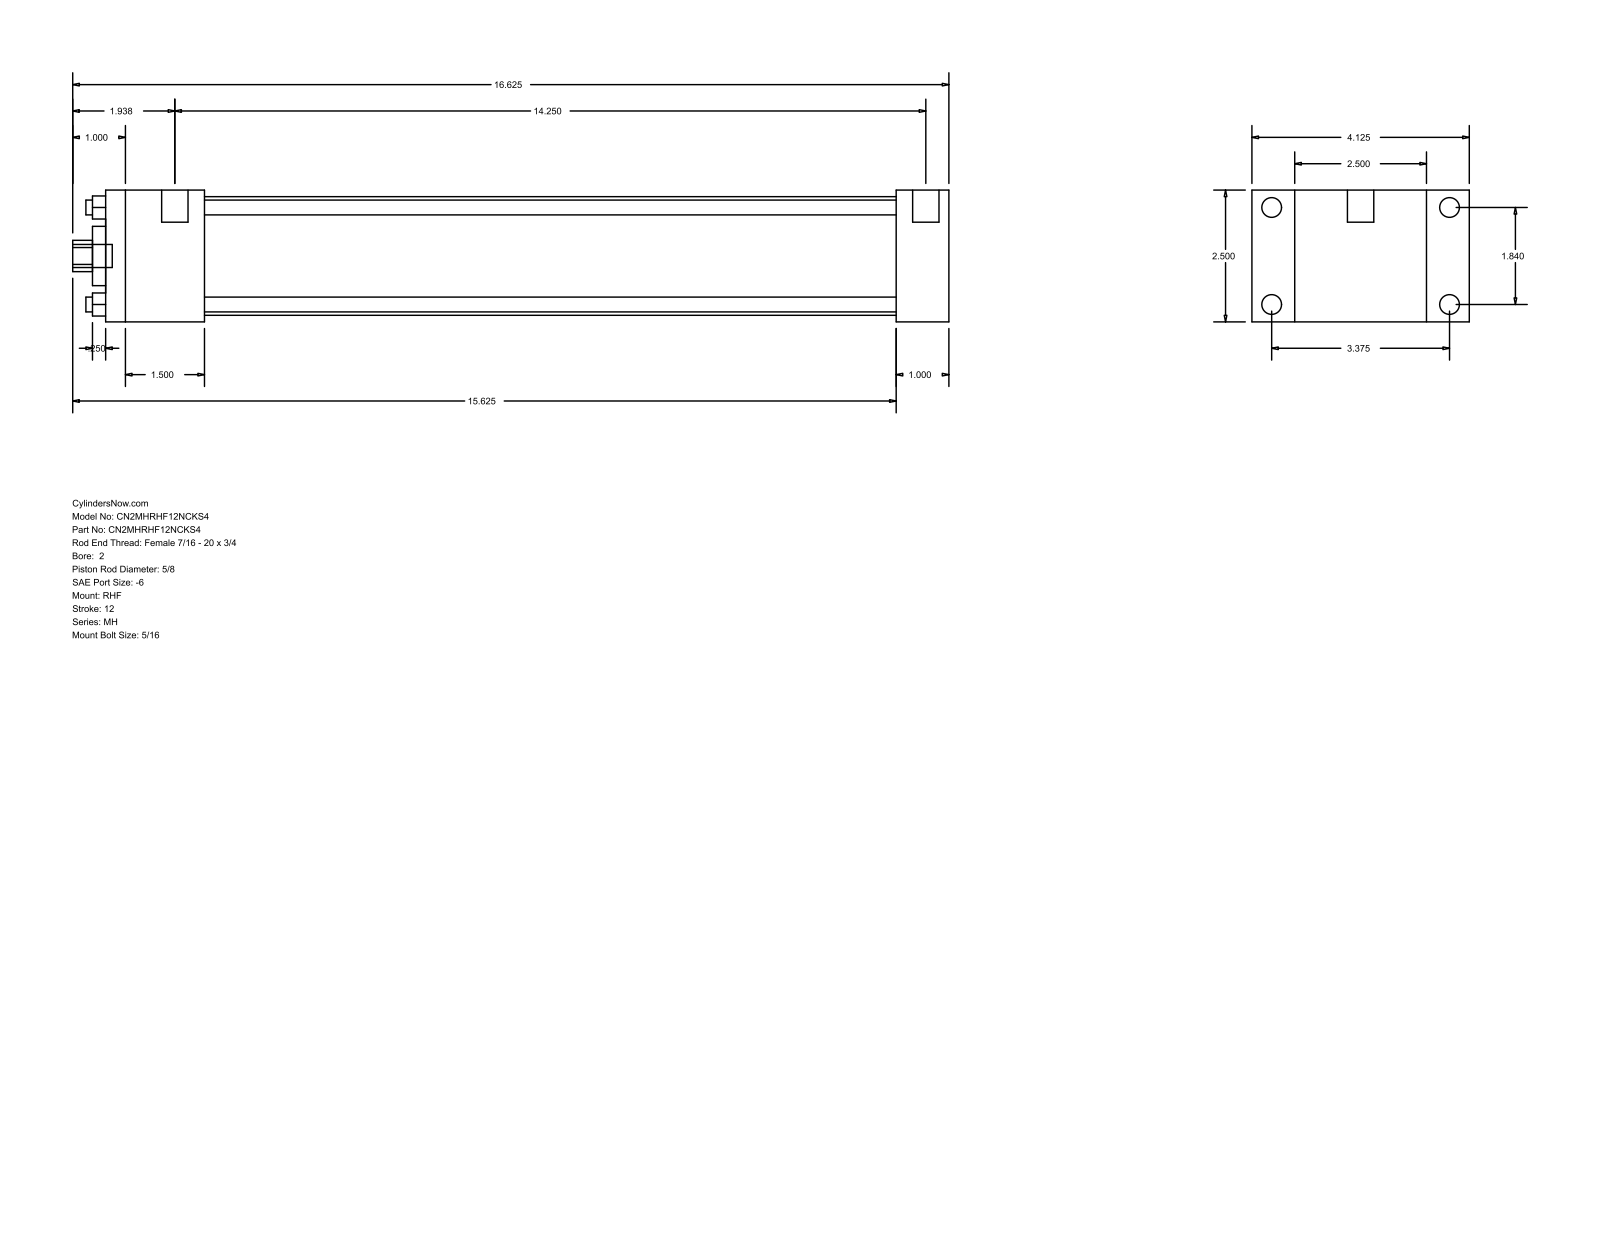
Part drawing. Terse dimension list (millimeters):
name: MH_RHF__0200_0.625
written by: GSSL Pune (CONFIG_CONTROL_DESIGN)
unit: mm
bodies: 0 solids, 88 faces (60 planar, 28 cylindrical, 0 other)
size: 422.27 × 104.78 × 63.5
holes: 4× ⌀7.14, 1× ⌀15.88, 1× ⌀28.57, 1× ⌀57.15
bosses: 4× ⌀9.53, 4× ⌀5.56, 2× ⌀12.7, 1× ⌀11.11
rounds: 1× R7.54
face distances: 63.5, 25.39, 20.64, 84.14, 381, 406.39, 104.78, 47.62, 333.38, 358.77
hole spacings: 33.05, 46.74, 66.1
